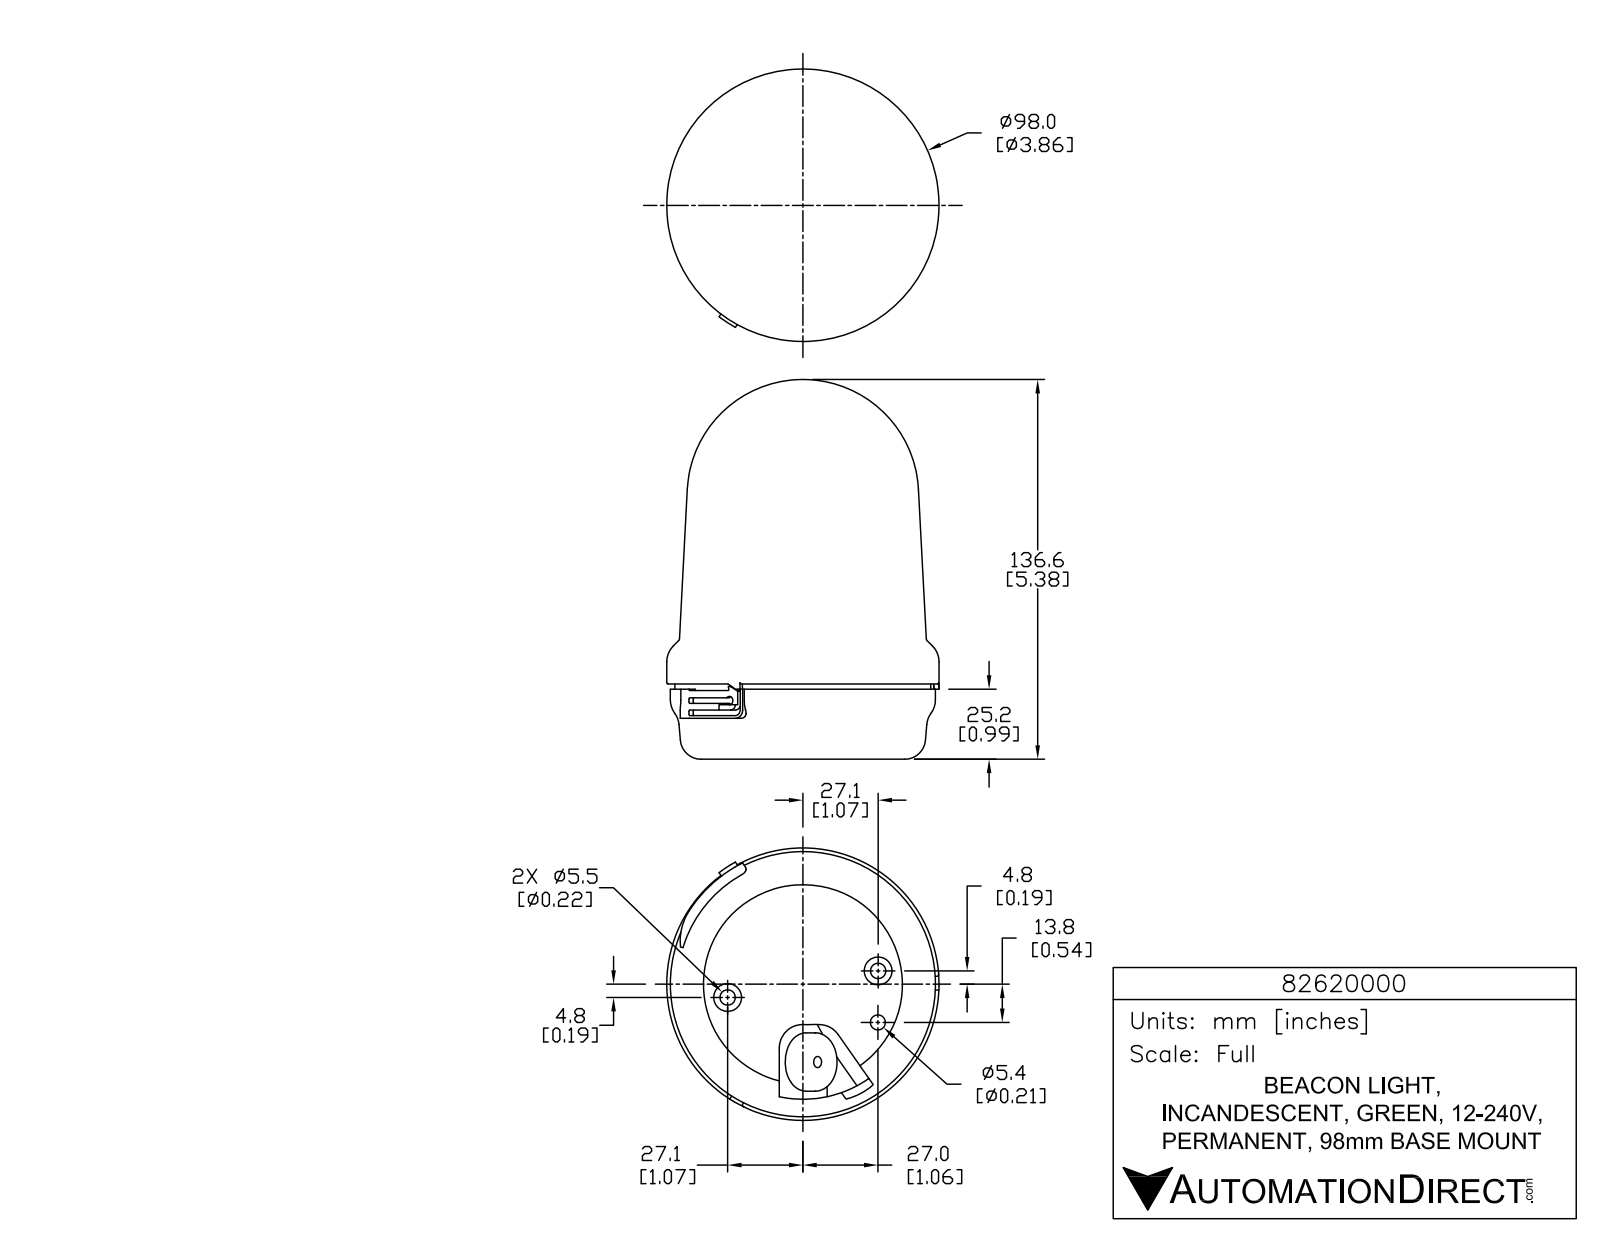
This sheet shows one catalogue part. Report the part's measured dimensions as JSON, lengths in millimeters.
{"part_name": "82620000", "step_written_by": "SolidWorks 2015 (AUTOMOTIVE_DESIGN)", "units": "millimeters", "bodies": {"solids": 1, "faces": 872, "planar": 566, "cylindrical": 204, "other": 102}, "overall_size": [136.6, 98, 98], "volume_mm3": 732300, "surface_area_mm2": 47520, "round_holes": [[1.5, 3], [5.5, 2], [4, 1], [5.4, 1], [71.6, 1]], "round_bosses_or_shafts": [[8.6, 3], [2.1, 3], [10, 2], [98, 1], [95.4, 1], [92.1, 1], [21, 1]], "partial_cylinders_radius": [[0.1, 9], [0.1, 6], [0.3, 6], [0.3, 6], [0.3, 6], [5, 6], [0.5, 5], [1, 4]], "face_to_face_distances": [26.5, 24.7, 1.9, 0.5, 25.2, 27.1, 6, 14.7, 14.2, 10.5], "hole_center_spacings": [27.5, 18.5, 30.3, 54.8, 55]}
